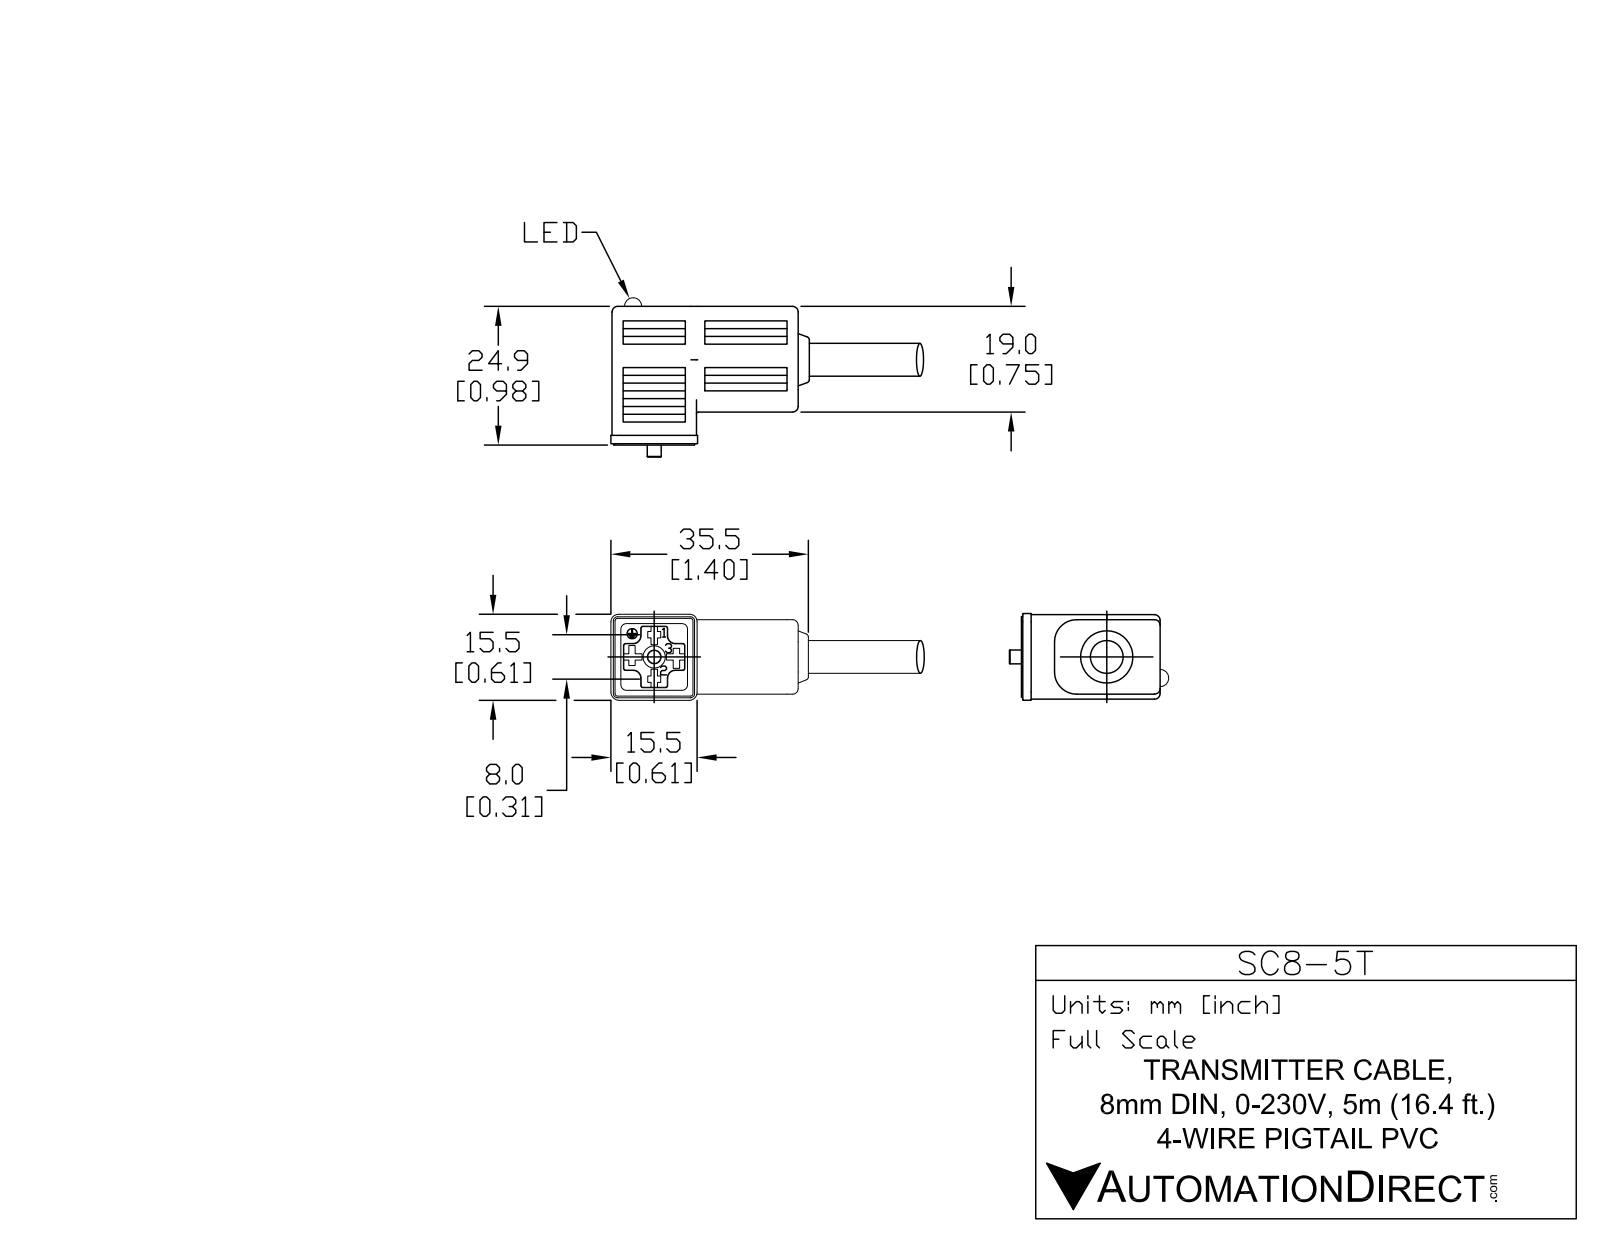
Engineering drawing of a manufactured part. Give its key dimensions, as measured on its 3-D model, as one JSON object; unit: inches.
{"part_name": "SC8-5T", "step_written_by": "SolidWorks 2011 (AUTOMOTIVE_DESIGN)", "units": "inches", "bodies": {"solids": 4, "faces": 334, "planar": 255, "cylindrical": 34, "other": 45}, "overall_size": [2.495, 1.323, 0.621], "volume_in3": 0.681, "surface_area_in2": 8.875, "round_holes": [[0.236, 2], [0.067, 1], [0.157, 1]], "round_bosses_or_shafts": [[0.226, 1], [0.108, 1]], "partial_cylinders_radius": [[0.02, 10], [0.03, 4], [0.079, 4], [0.01, 3], [0.157, 2]], "face_to_face_distances": [0.876, 0.039, 0.035, 0.61, 0.915, 0.564, 0.541, 0.059, 0.118, 0.157], "hole_center_spacings": [0.133]}
